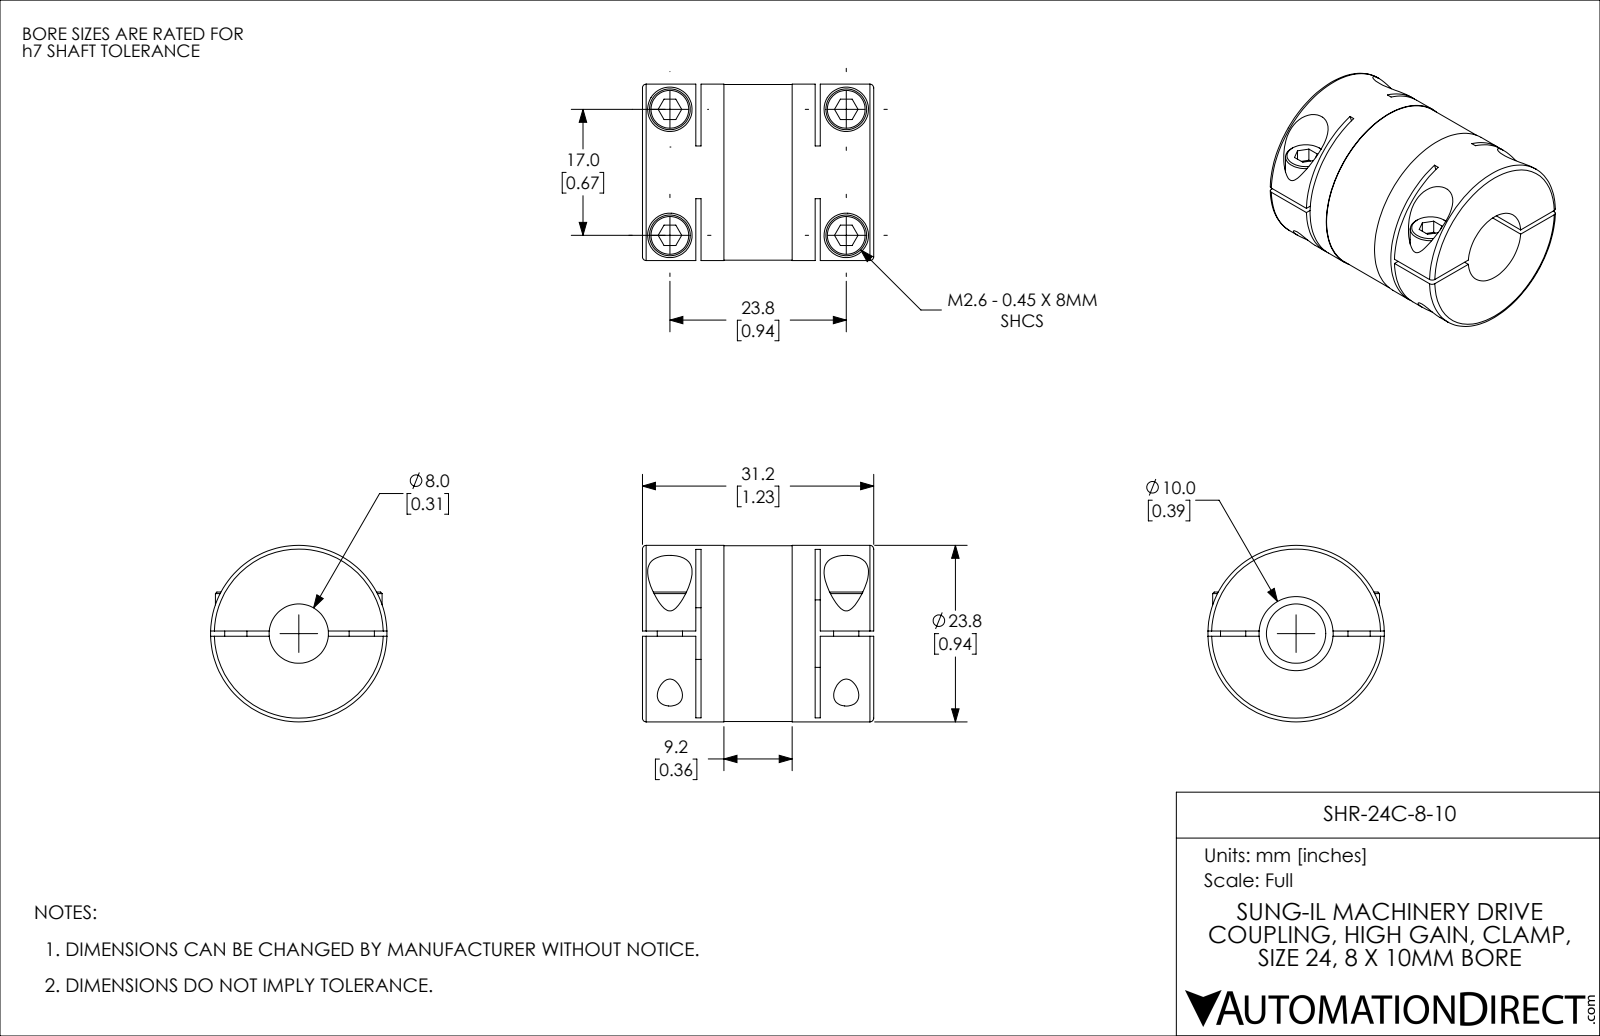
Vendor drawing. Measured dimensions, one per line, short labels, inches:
name: SHR-24C-8-10
written by: SolidWorks 2021 (CONFIG_CONTROL_DESIGN)
unit: in
bodies: 1 solid, 146 faces (70 planar, 56 cylindrical, 20 other)
size: 1.228 × 0.937 × 0.937
volume: 0.632 in³; area: 10.12 in²
holes: 4× ⌀0.134, 4× ⌀0.236, 1× ⌀0.315, 1× ⌀0.394, 1× ⌀0.472
bosses: 4× ⌀0.217, 2× ⌀0.118, 1× ⌀0.937, 1× ⌀0.933
rounds: 2× R1.476
face distances: 0.028, 0.311, 0.917, 0.283, 0.945, 0.634, 1.228, 0.606, 0.661, 0.433
hole spacings: 0.669, 0.937, 1.152
